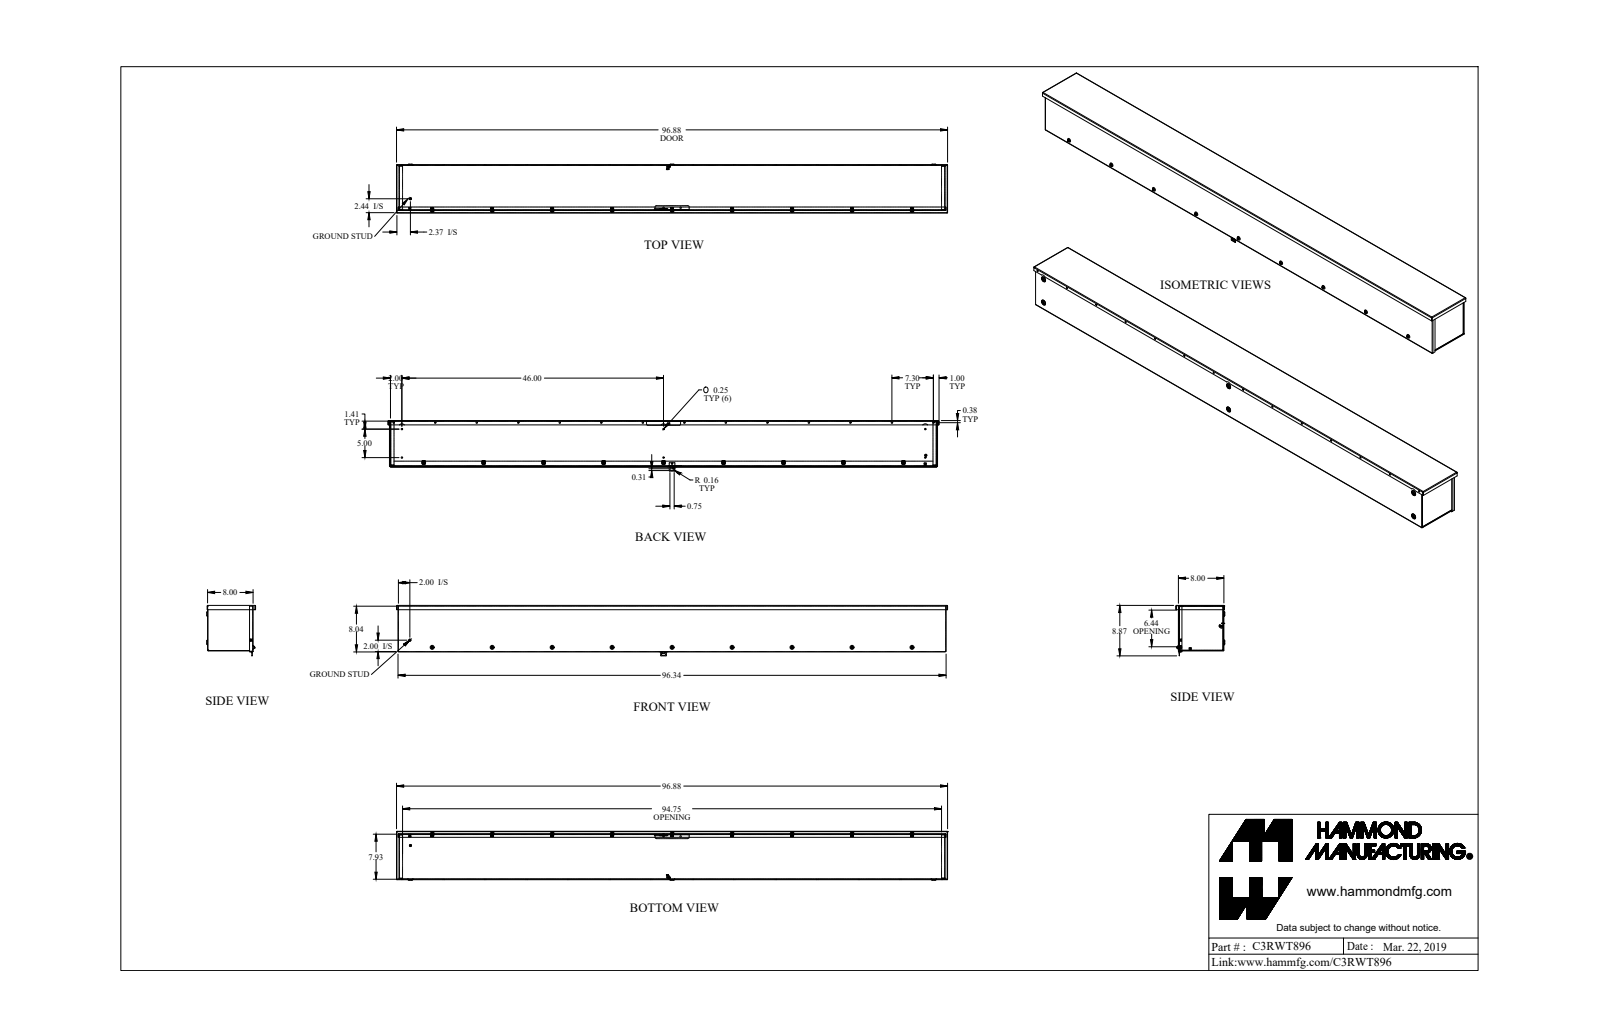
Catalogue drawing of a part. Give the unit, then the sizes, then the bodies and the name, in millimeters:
Units: millimetres
Overall size (bounding box): 2460.6 × 225.3 × 218.3
Round holes (diameter × count): ⌀6.4 ×22, ⌀4 ×11, ⌀5.4 ×9, ⌀5.8 ×9, ⌀5.2 ×2, ⌀3.2 ×1, ⌀3.5 ×1, ⌀5.1 ×1, ⌀5.5 ×1
Round bosses / shafts (diameter × count): ⌀4.8 ×10, ⌀3.8 ×9, ⌀9.5 ×2, ⌀12.7 ×1, ⌀9.3 ×1, ⌀5.3 ×1, ⌀3.9 ×1, ⌀3.2 ×1
Partial cylindrical surfaces — rounded edges, fillets, slot ends (radius × count): R2 ×36, R2.7 ×36, R0.6 ×18, R0.9 ×18, R2.7 ×18, R3.2 ×17, R4.3 ×9, R5.2 ×9
Main face-to-face distances: 1.8, 201.4, 203.2, 1.8, 199.5, 199.5, 201.4, 3.7, 212.5, 13
Hole centre spacings: 185.4, 267.8, 370.7, 178.1, 535.6, 556.1, 633.2, 803.4
Volume: 4 192 000 mm³ · Surface area: 4 631 000 mm²
Bodies: 41 solids, 1569 faces (854 planar, 503 cylindrical, 212 other)
Part name (STEP PRODUCT): C3RWT896_Default
STEP written by: SolidWorks 2019 (CONFIG_CONTROL_DESIGN)
